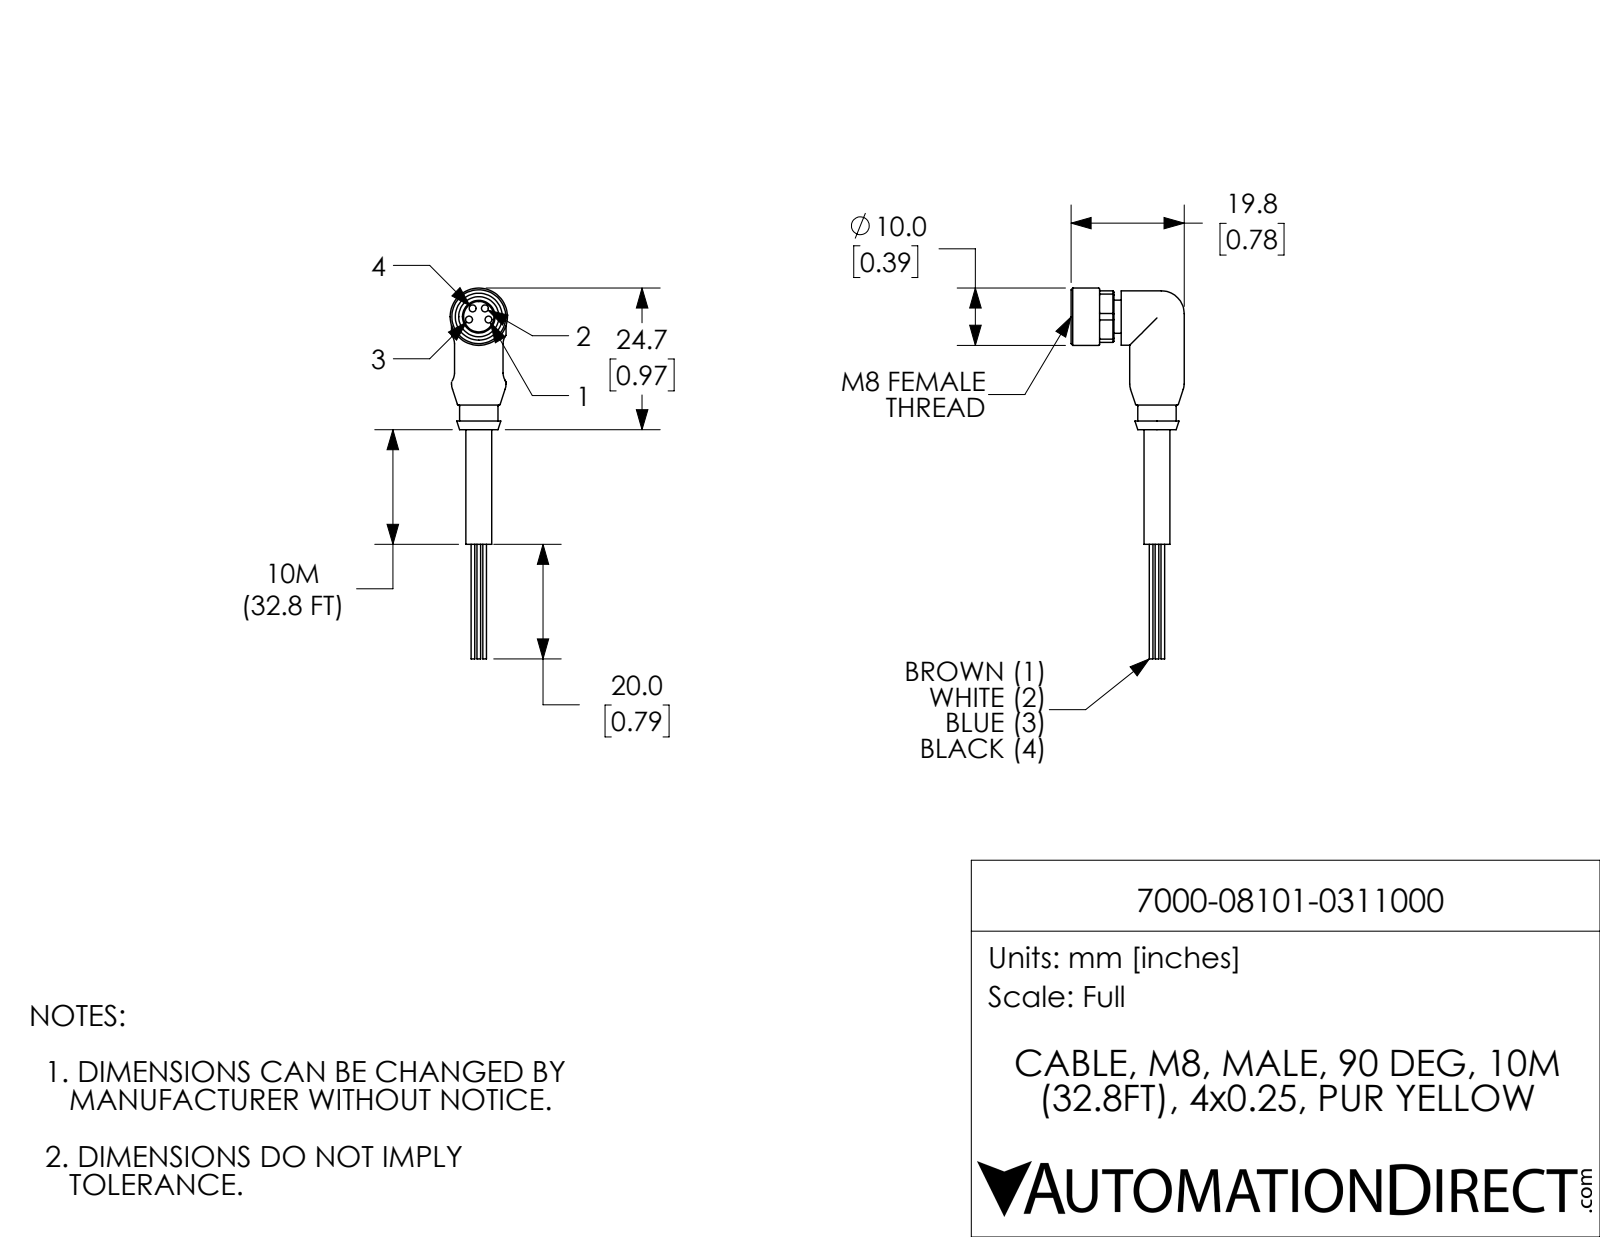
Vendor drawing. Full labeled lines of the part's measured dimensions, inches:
Part name (STEP PRODUCT): 7000-08101-0311000
STEP written by: SolidWorks 2021 (CONFIG_CONTROL_DESIGN)
Units: inches
Bodies: 5 solids, 117 faces (41 planar, 47 cylindrical, 29 other)
Overall size (bounding box): 2.548 × 0.778 × 0.394
Volume: 0.147 in³ · Surface area: 2.976 in²
Round holes (diameter × count): ⌀0.047 ×4, ⌀0.276 ×1
Round bosses / shafts (diameter × count): ⌀0.025 ×3, ⌀0.374 ×2, ⌀0.394 ×1, ⌀0.264 ×1, ⌀0.228 ×1, ⌀0.224 ×1, ⌀0.177 ×1, ⌀0.025 ×1
Partial cylindrical surfaces — rounded edges, fillets, slot ends (radius × count): R0.008 ×4, R0.098 ×4, R0.193 ×1
Main face-to-face distances: 0.049, 0.354, 0.059, 0.335, 0.028, 0.787, 0.268, 0.317, 0.295, 0.344
Hole centre spacings: 0.07, 0.071, 0.081, 0.133, 0.084, 0.134
